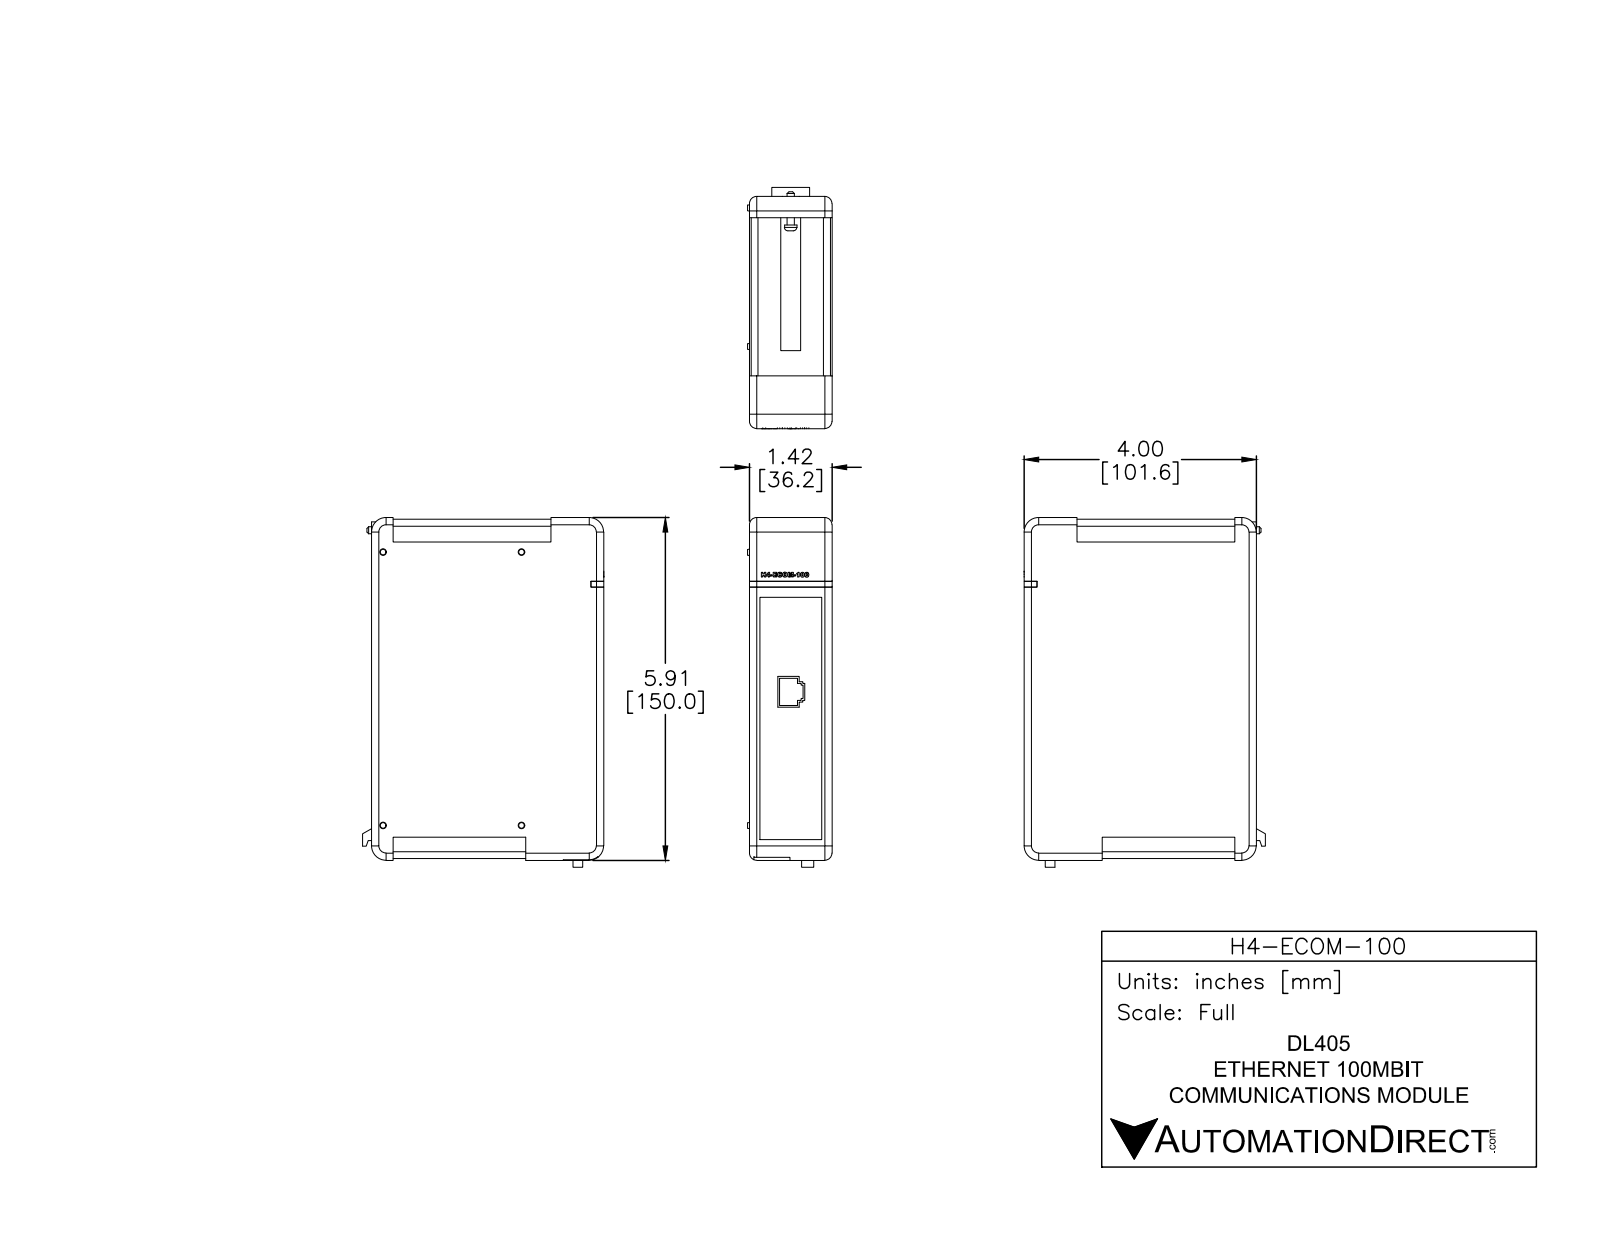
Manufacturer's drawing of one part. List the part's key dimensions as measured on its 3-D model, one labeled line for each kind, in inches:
Part name (STEP PRODUCT): H4-ECOM-100
STEP written by: SolidWorks 2014 (AUTOMOTIVE_DESIGN)
Units: inches
Bodies: 2 solids, 294 faces (201 planar, 34 cylindrical, 59 other)
Overall size (bounding box): 6.025 × 4.156 × 1.455
Volume: 32.09 in³ · Surface area: 81.27 in²
Round bosses / shafts (diameter × count): ⌀0.212 ×1, ⌀0.123 ×1
Partial cylindrical surfaces — rounded edges, fillets, slot ends (radius × count): R0.125 ×8, R0.12 ×4, R0.25 ×4, R0.145 ×1, R0.171 ×1
Main face-to-face distances: 1.425, 0.03, 3.97, 1.395, 5.845, 5.875, 4, 0.2, 3.77, 3.8
